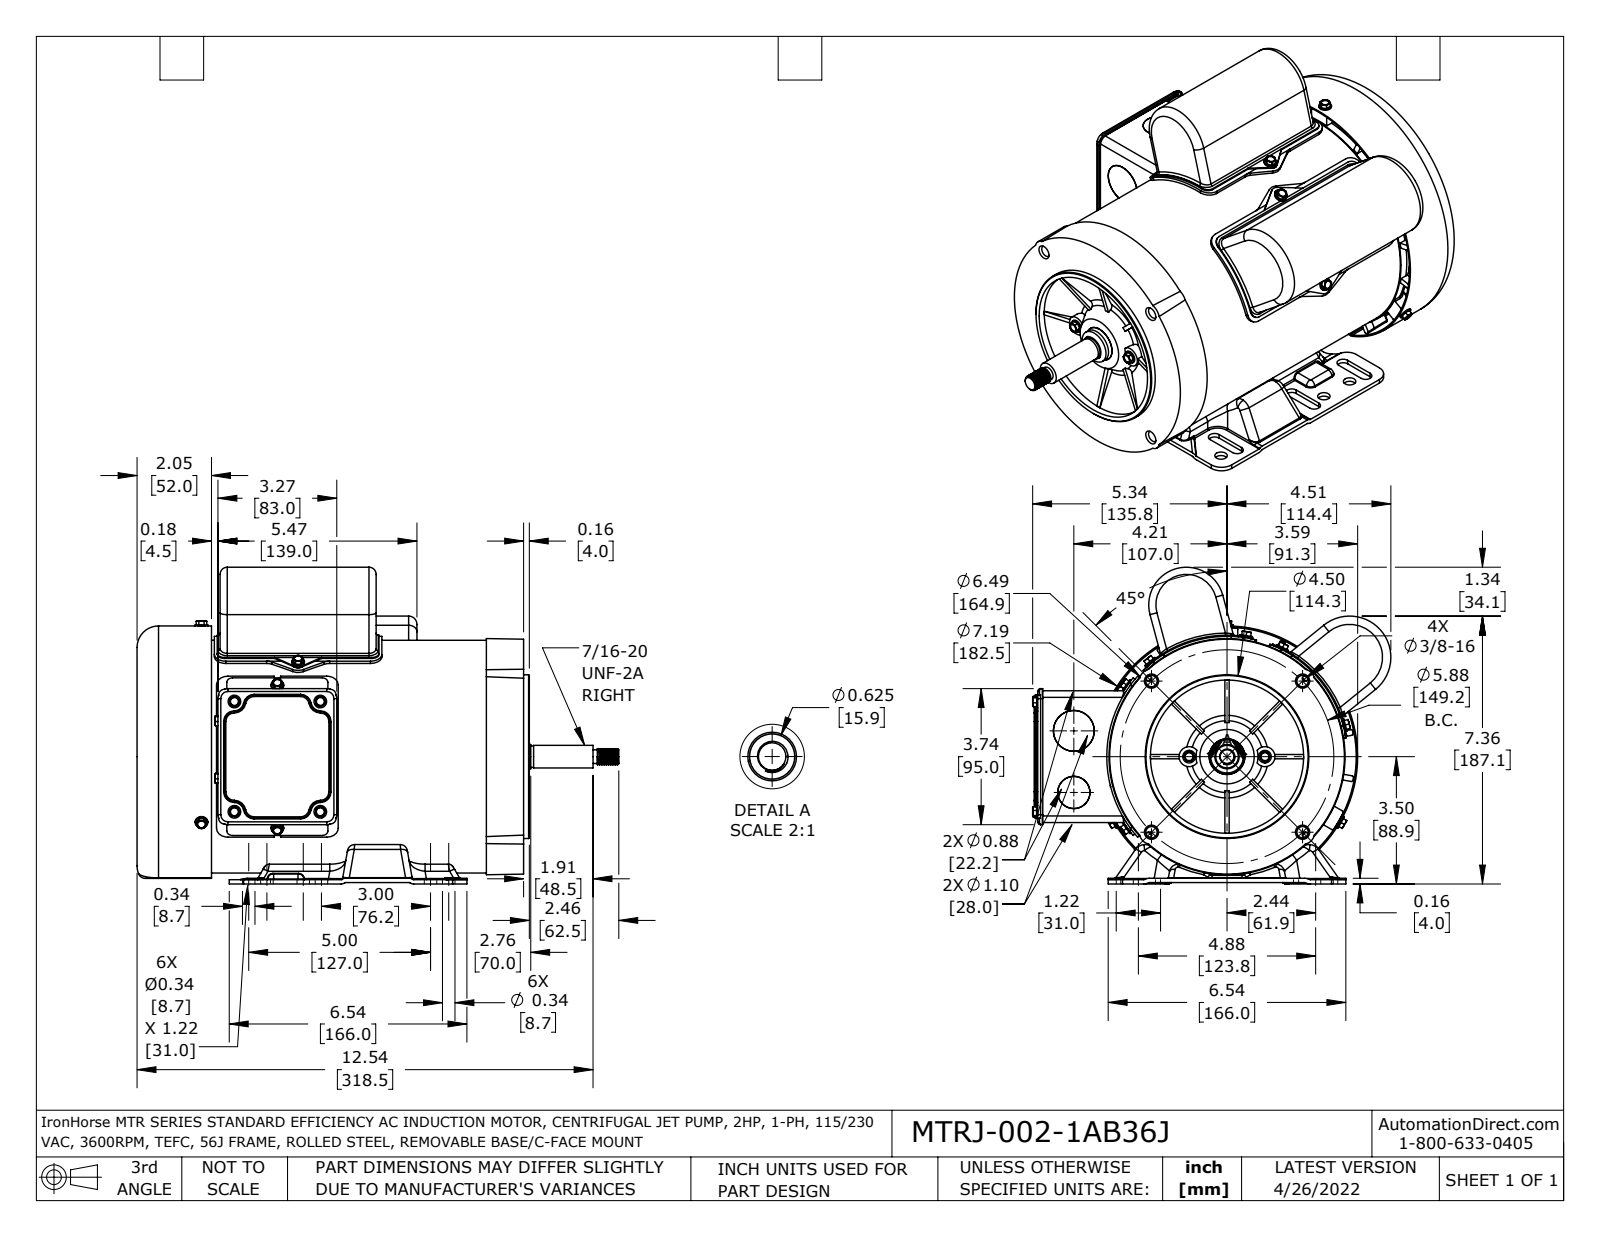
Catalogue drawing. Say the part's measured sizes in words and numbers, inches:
The part is named "MTRJ-002-1AB36J redcmb1 coord". Its 3-D file was written by "SolidWorks 2021 (AUTOMOTIVE_DESIGN)". It is 39 solids with 3106 faces: 781 planar, 1029 cylindrical and 1296 other. Overall it measures 13.248 by 9.851 by 8.707 inches. Its volume is 52.28 cubic inches and its surface area 1 142 square inches. Round holes: 17 of diameter 0.219, 12 of diameter 0.197, 9 of diameter 0.136, 8 of diameter 0.276, 6 of diameter 0.177, 6 of diameter 0.217, 6 of diameter 0.328, 6 of diameter 0.344, 4 of diameter 0.15, 4 of diameter 0.313, 4 of diameter 0.709, 2 of diameter 0.134. Round bosses or shafts: 17 of diameter 0.164, 14 of diameter 0.348, 6 of diameter 0.236, 3 of diameter 0.348, 1 of diameter 7.185, 1 of diameter 6.398, 1 of diameter 4.5, 1 of diameter 1.535. Partial cylindrical surfaces (rounded edges, fillets, slot ends): 117 of radius 0.118, 57 of radius 0.039, 32 of radius 0.157, 30 of radius 0.02, 26 of radius 0.138, 24 of radius 0.197, 20 of radius 0.228, 18 of radius 0.079. The main face-to-face distances are 0.031, 0.039, 0.118, 0.063, 10.63, 10.591, 0.157, 3.559, 3.087, 0.079. The hole center spacings are 4.221, 3.031, 0.094, 2.32, 2.409, 2.937, 3.748, 3.841.
